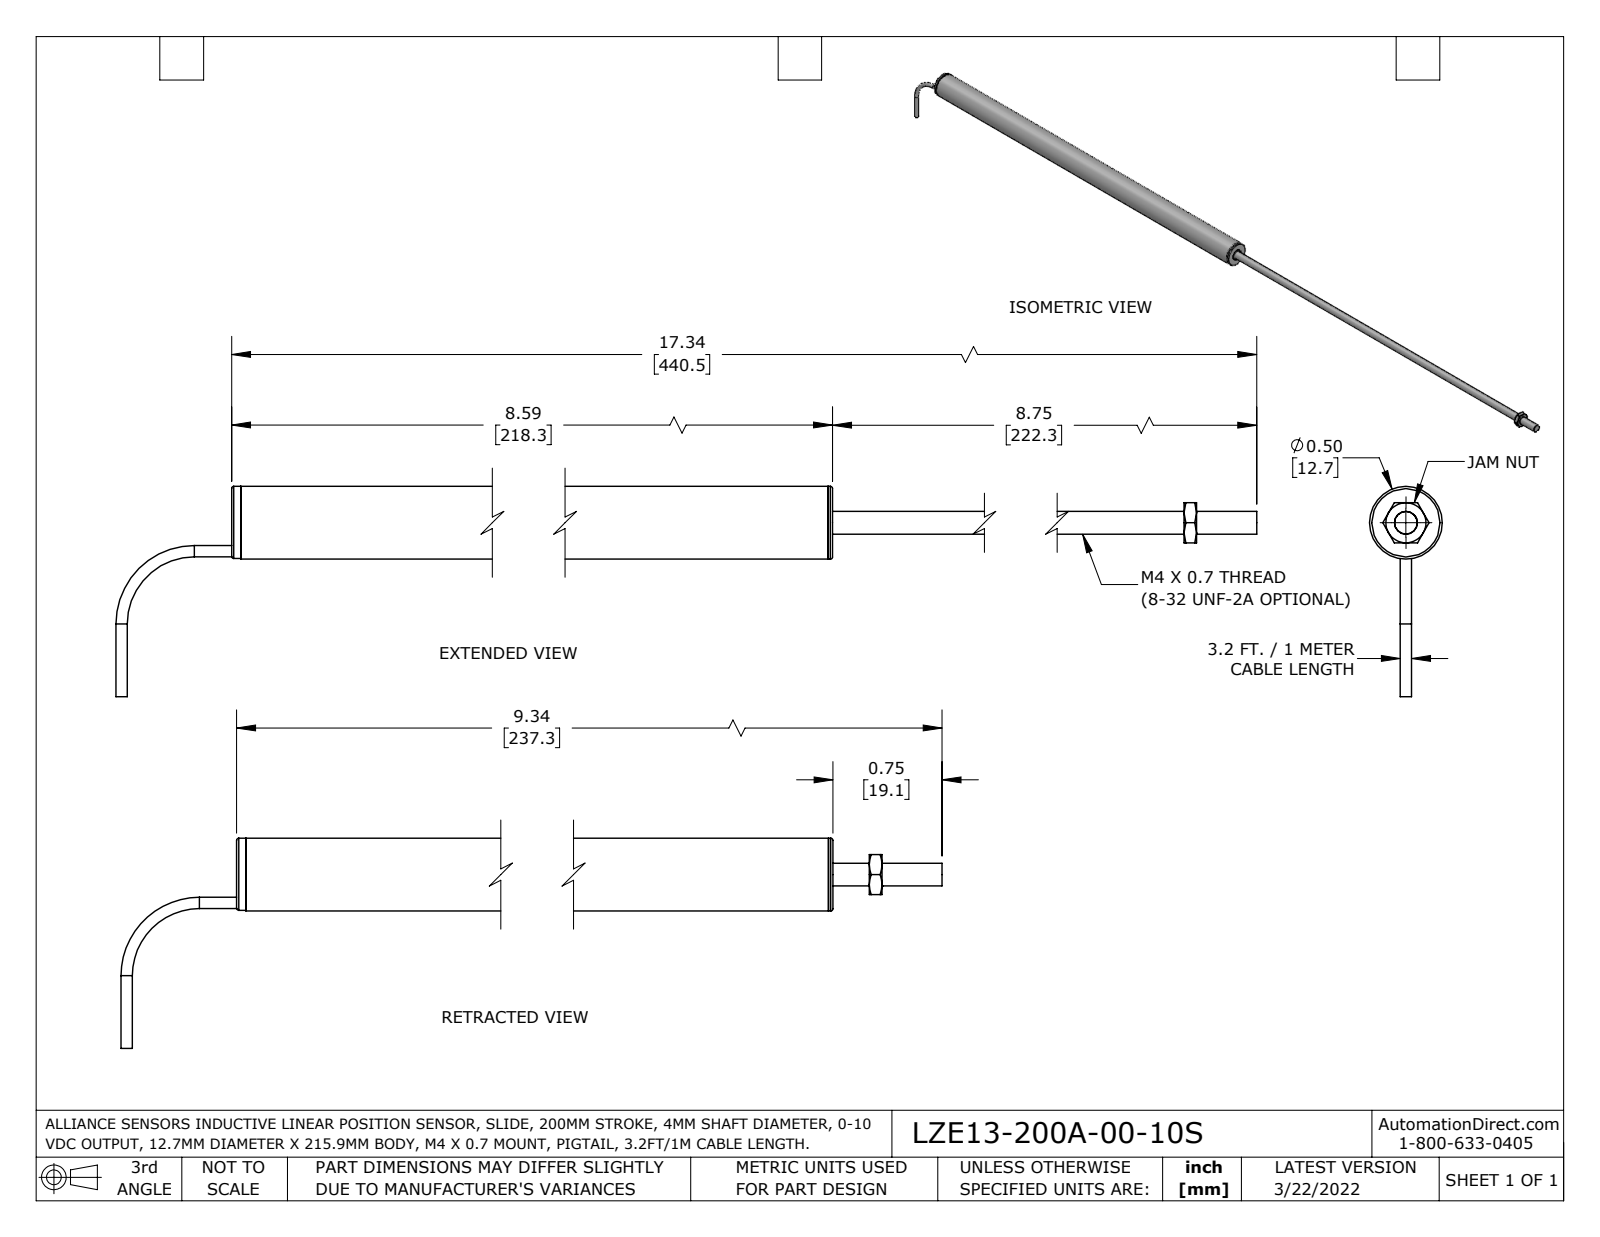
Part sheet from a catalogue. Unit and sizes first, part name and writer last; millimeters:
Units: millimetres
Overall size (bounding box): 460.7 × 36.7 × 12.7
Round holes (diameter × count): ⌀2 ×1, ⌀4 ×1, ⌀4.7 ×1, ⌀5.7 ×1
Round bosses / shafts (diameter × count): ⌀12.7 ×1, ⌀11.9 ×1, ⌀5.6 ×1, ⌀4 ×1, ⌀2.5 ×1, ⌀2 ×1
Partial cylindrical surfaces — rounded edges, fillets, slot ends (radius × count): R1.2 ×1
Main face-to-face distances: 2, 215.9, 0.8, 1.6, 7, 218.3, 216.7, 214.3, 2.4, 215.1
Hole centre spacings: 5
Volume: 8 820 mm³ · Surface area: 28 430 mm²
Bodies: 9 solids, 98 faces (32 planar, 38 cylindrical, 28 other)
Part name (STEP PRODUCT): 5500-0029; 5300-0002; 3120-0033-XX_3120-0033-08; 3120-0032 (+6 more)
STEP written by: SolidWorks 2021 (AUTOMOTIVE_DESIGN)
